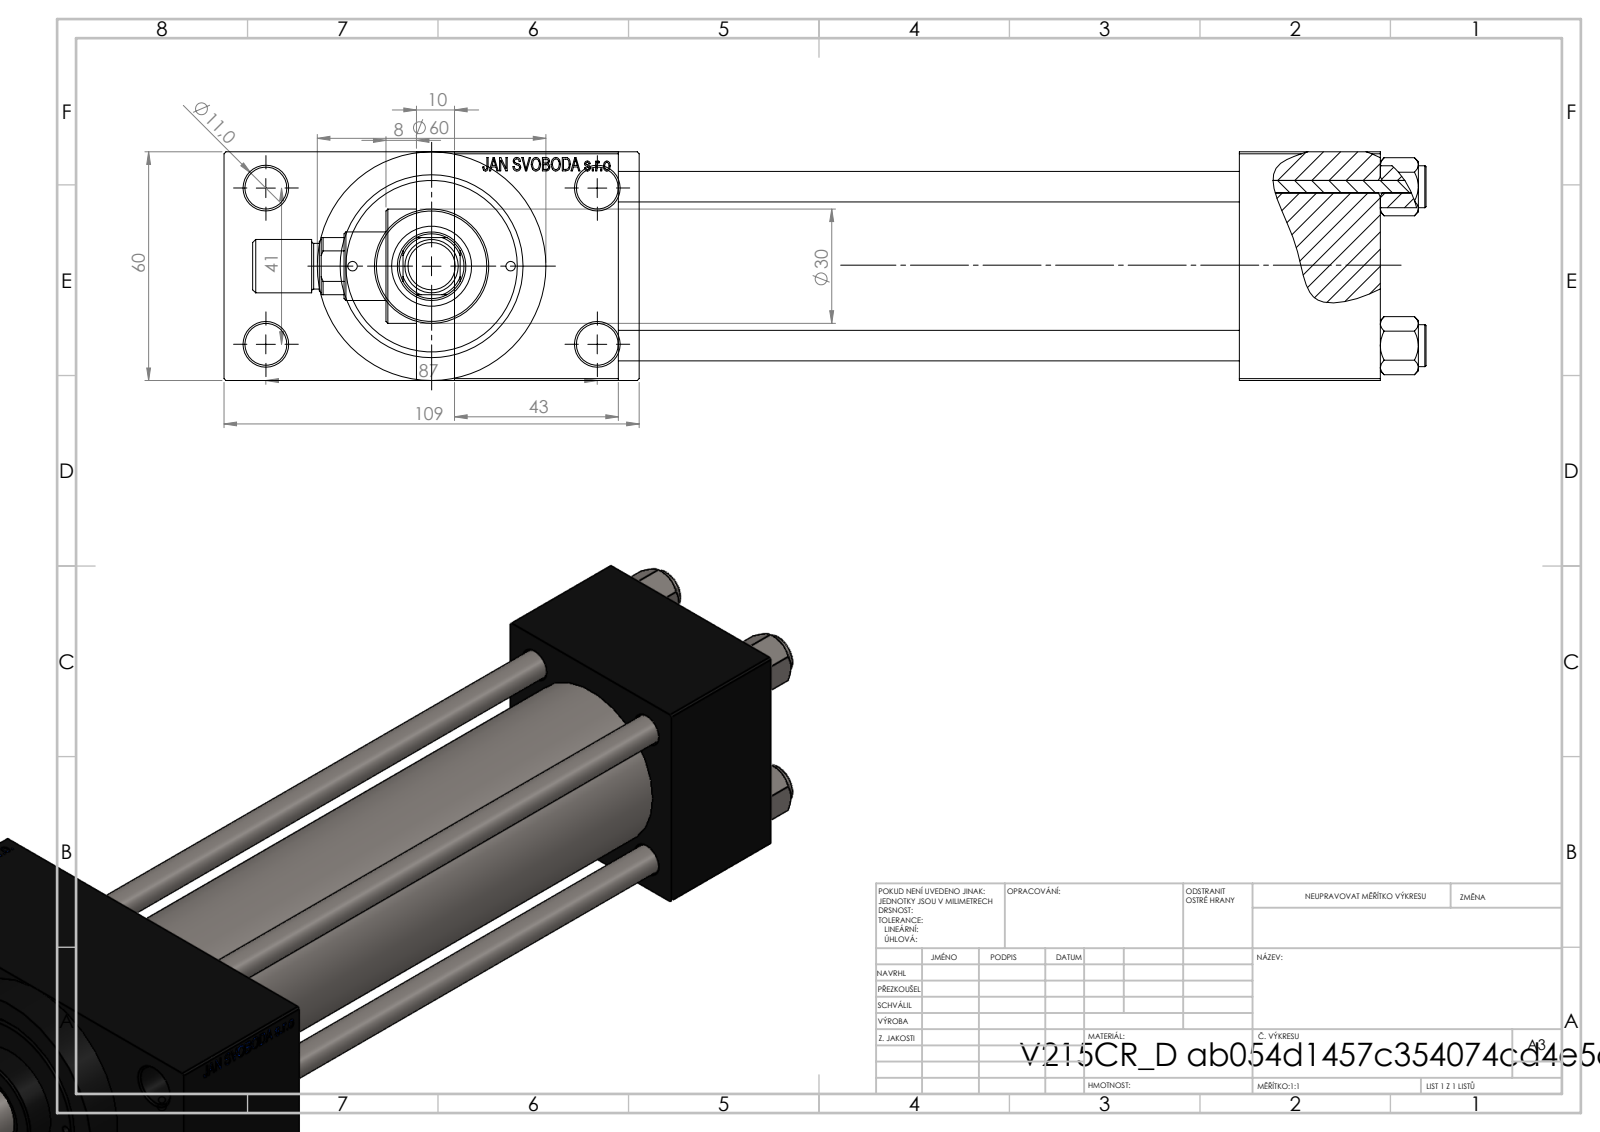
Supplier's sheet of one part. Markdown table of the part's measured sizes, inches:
| quantity | value |
| --- | --- |
| part name | NUT_M5_D; V215CR_VCP_D; V215CR_D_Body; ROD_END_AH (+2 more) |
| STEP written by | SolidWorks 2019 (CONFIG_CONTROL_DESIGN) |
| units | inches |
| bodies | 12 solids, 1126 faces (504 planar, 96 cylindrical, 526 other) |
| overall size | 12.126 × 4.291 × 2.362 |
| volume | 36.94 in³ |
| surface area | 261.2 in² |
| round holes (diameter × count) | 0.315 × 4, 0.433 × 4, 0.098 × 2, 0.276 × 2, 0.656 × 2, 0.945 × 2, 0.335 × 1, 0.709 × 1, 0.827 × 1, 1.22 × 1, 1.575 × 1, 1.772 × 1 |
| round bosses / shafts (diameter × count) | 0.433 × 4, 2.362 × 1, 1.811 × 1, 1.181 × 1, 0.551 × 1, 0.472 × 1 |
| partial cylindrical surfaces (radius × count) | 0.335 × 1 |
| main face-to-face distances | 2.362, 6.417, 0.965, 3.327, 1.457, 7.874, 1.693, 9.567, 8.11, 8.257 |
| hole center spacings | 0.821, 0.892, 1.161, 1.206, 1.642, 1.832, 1.856, 1.893 |
